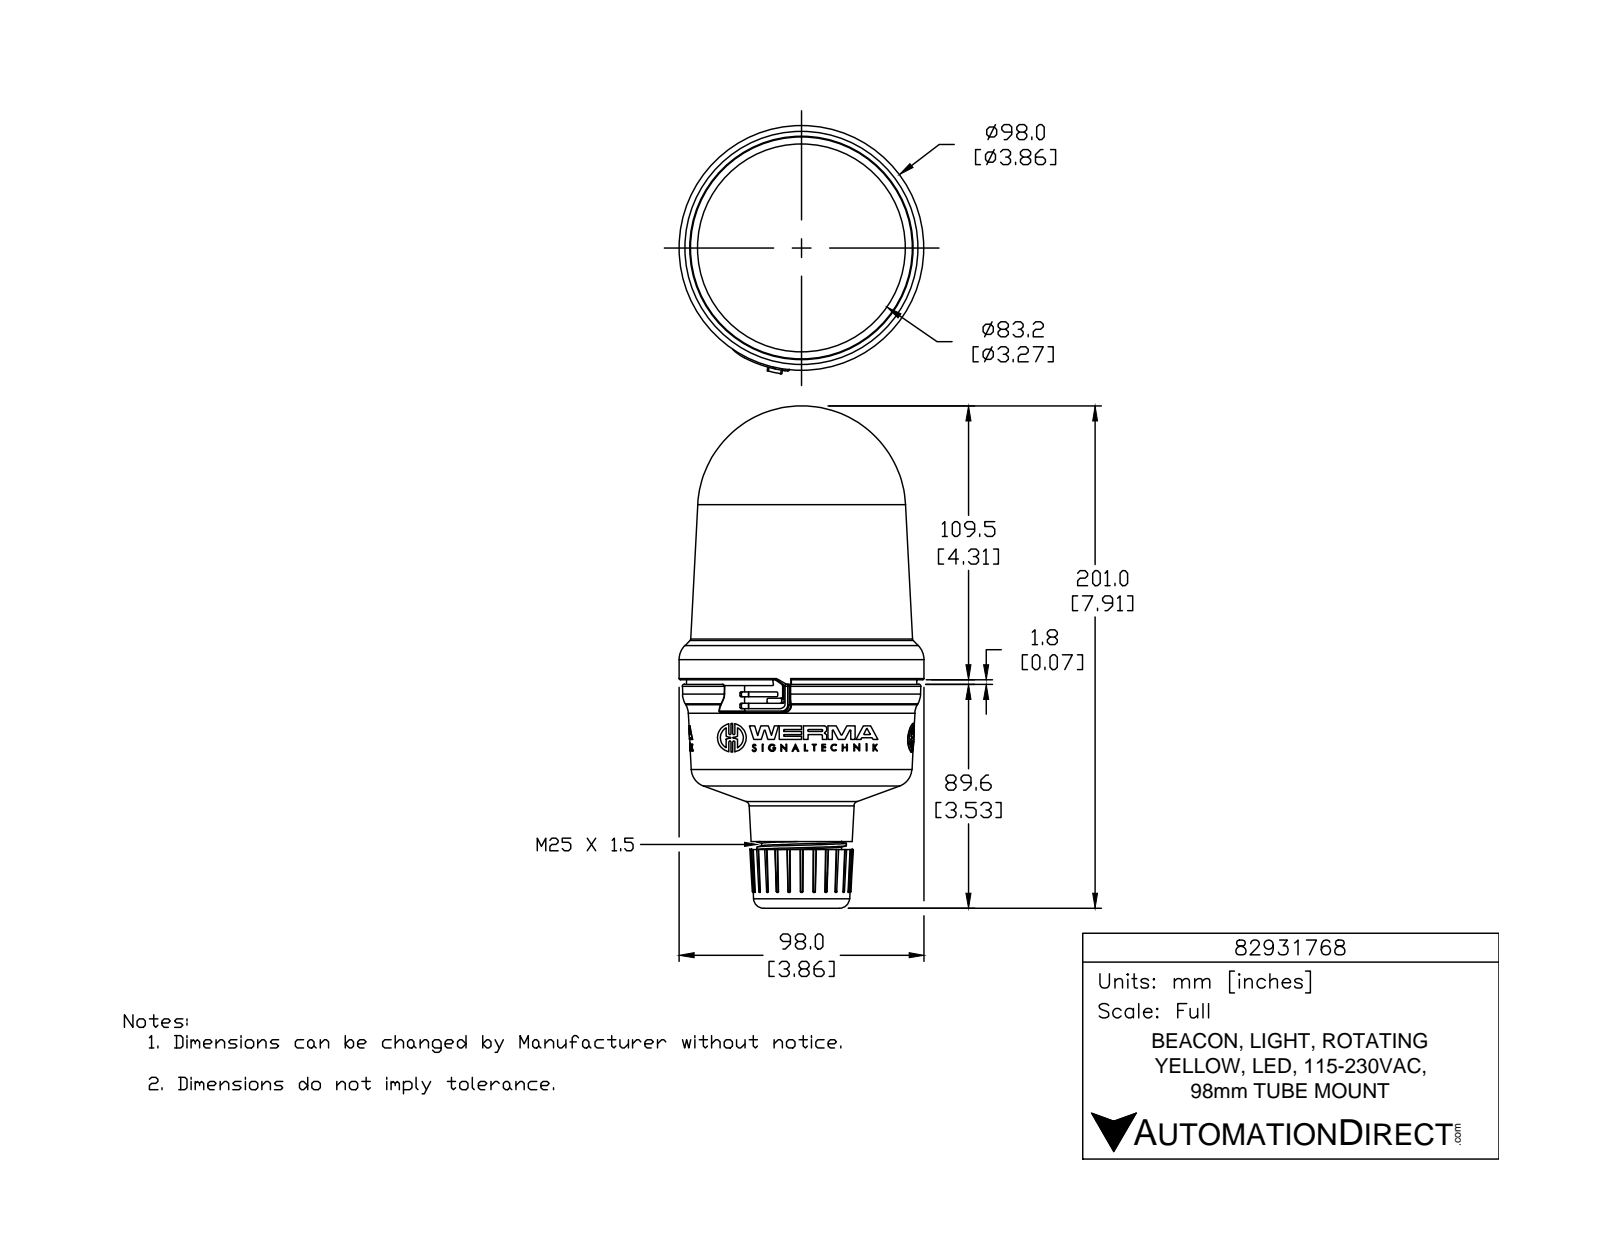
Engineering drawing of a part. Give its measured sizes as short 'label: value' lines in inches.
name: 82931768
written by: SolidWorks 2015 (AUTOMOTIVE_DESIGN)
unit: in
bodies: 1 solid, 1006 faces (554 planar, 189 cylindrical, 263 other)
size: 7.914 × 3.912 × 3.858
volume: 54.7 in³; area: 91.39 in²
holes: 3× ⌀0.078, 1× ⌀1.013, 1× ⌀1.024
bosses: 3× ⌀0.452, 3× ⌀0.113, 1× ⌀3.858, 1× ⌀1.409, 1× ⌀1.261
rounds: 12× R0.02, 9× R0.007, 6× R0.007, 6× R0.016, 6× R0.016, 6× R0.016, 6× R0.262, 3× R0.006
face distances: 2.214, 0.462, 2.676, 0.335, 0.127, 2.548, 2.603, 2.476, 2.141, 0.073
